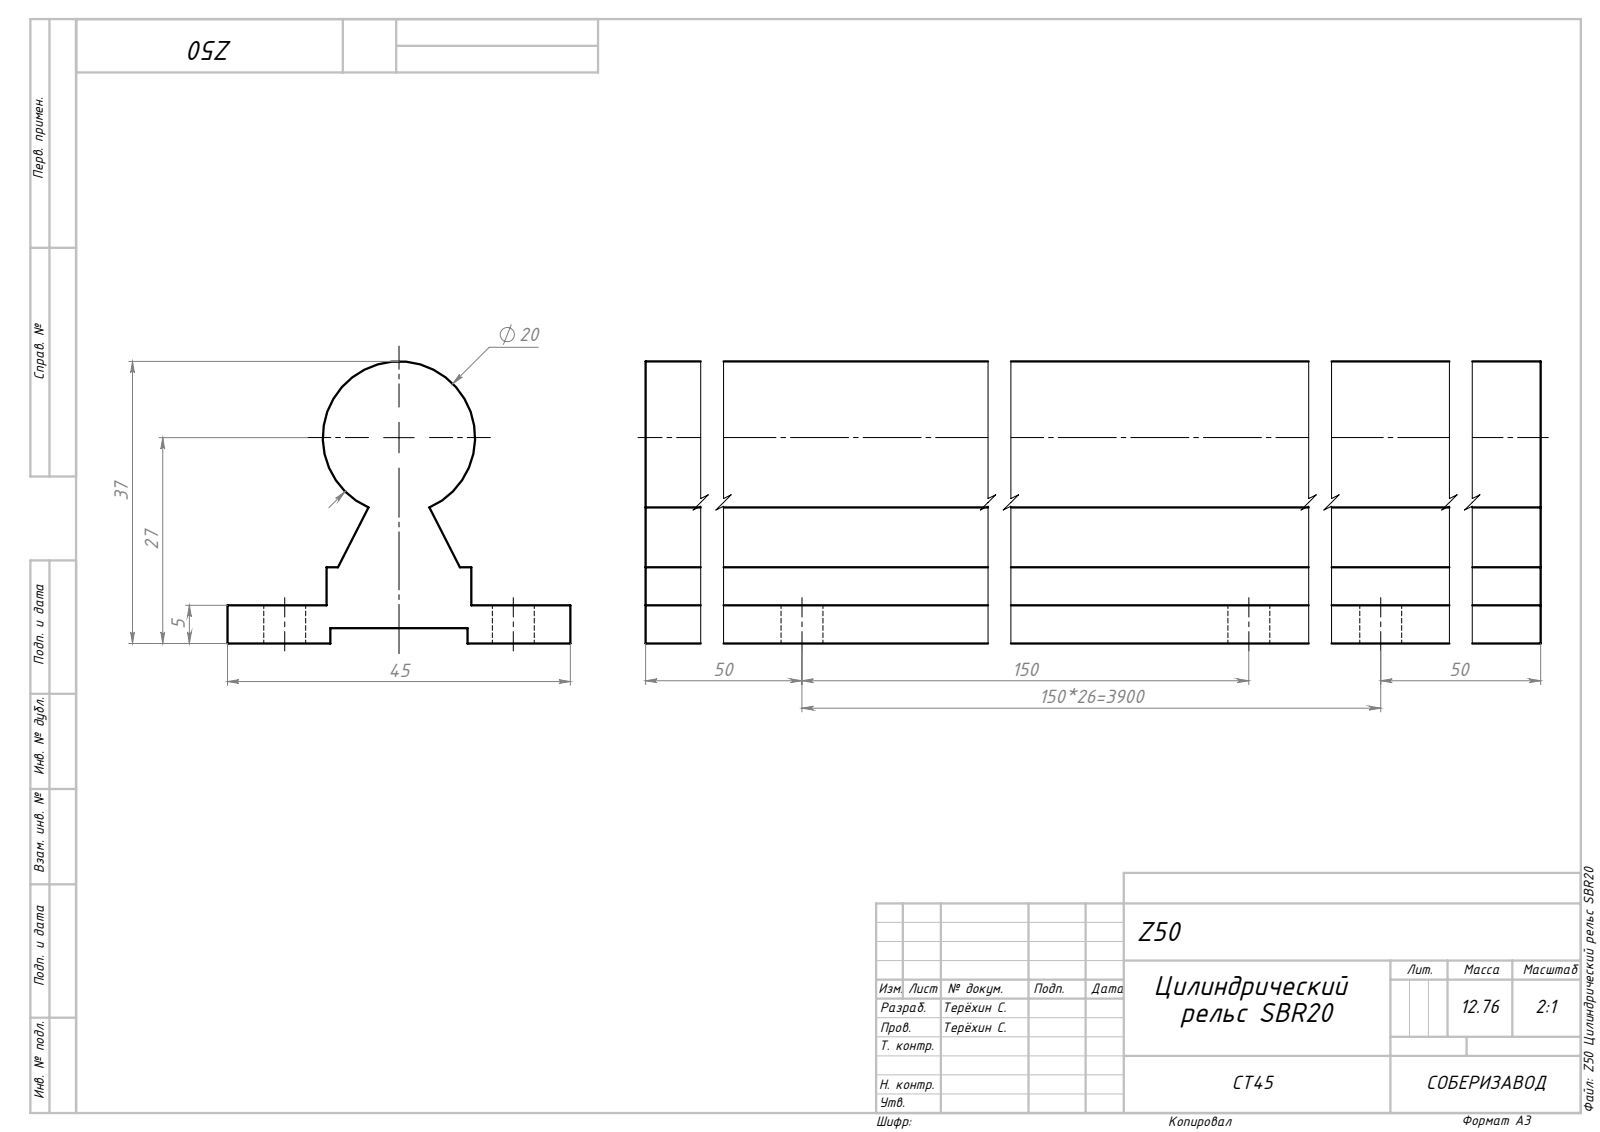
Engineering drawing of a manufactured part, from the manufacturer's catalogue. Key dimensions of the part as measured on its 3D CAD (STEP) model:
Part name (STEP PRODUCT): Z50 Цилиндрический рельс SBR20_00; Сборка3
STEP written by: SolidWorks 2022 (AUTOMOTIVE_DESIGN)
Units: millimetres
Bodies: 1 solid, 128 faces (17 planar, 111 cylindrical, 0 other)
Overall size (bounding box): 4000 × 45 × 37
Volume: 2 744 000 mm³ · Surface area: 684 256 mm²
Round holes (diameter × count): ⌀5.5 ×54
Round bosses / shafts (diameter × count): ⌀20 ×1
Main face-to-face distances: 5, 2, 3, 13, 32, 45, 19, 13.5, 31.5, 0.5
Hole centre spacings: 150, 300, 450, 600, 750, 900, 1050, 1200
